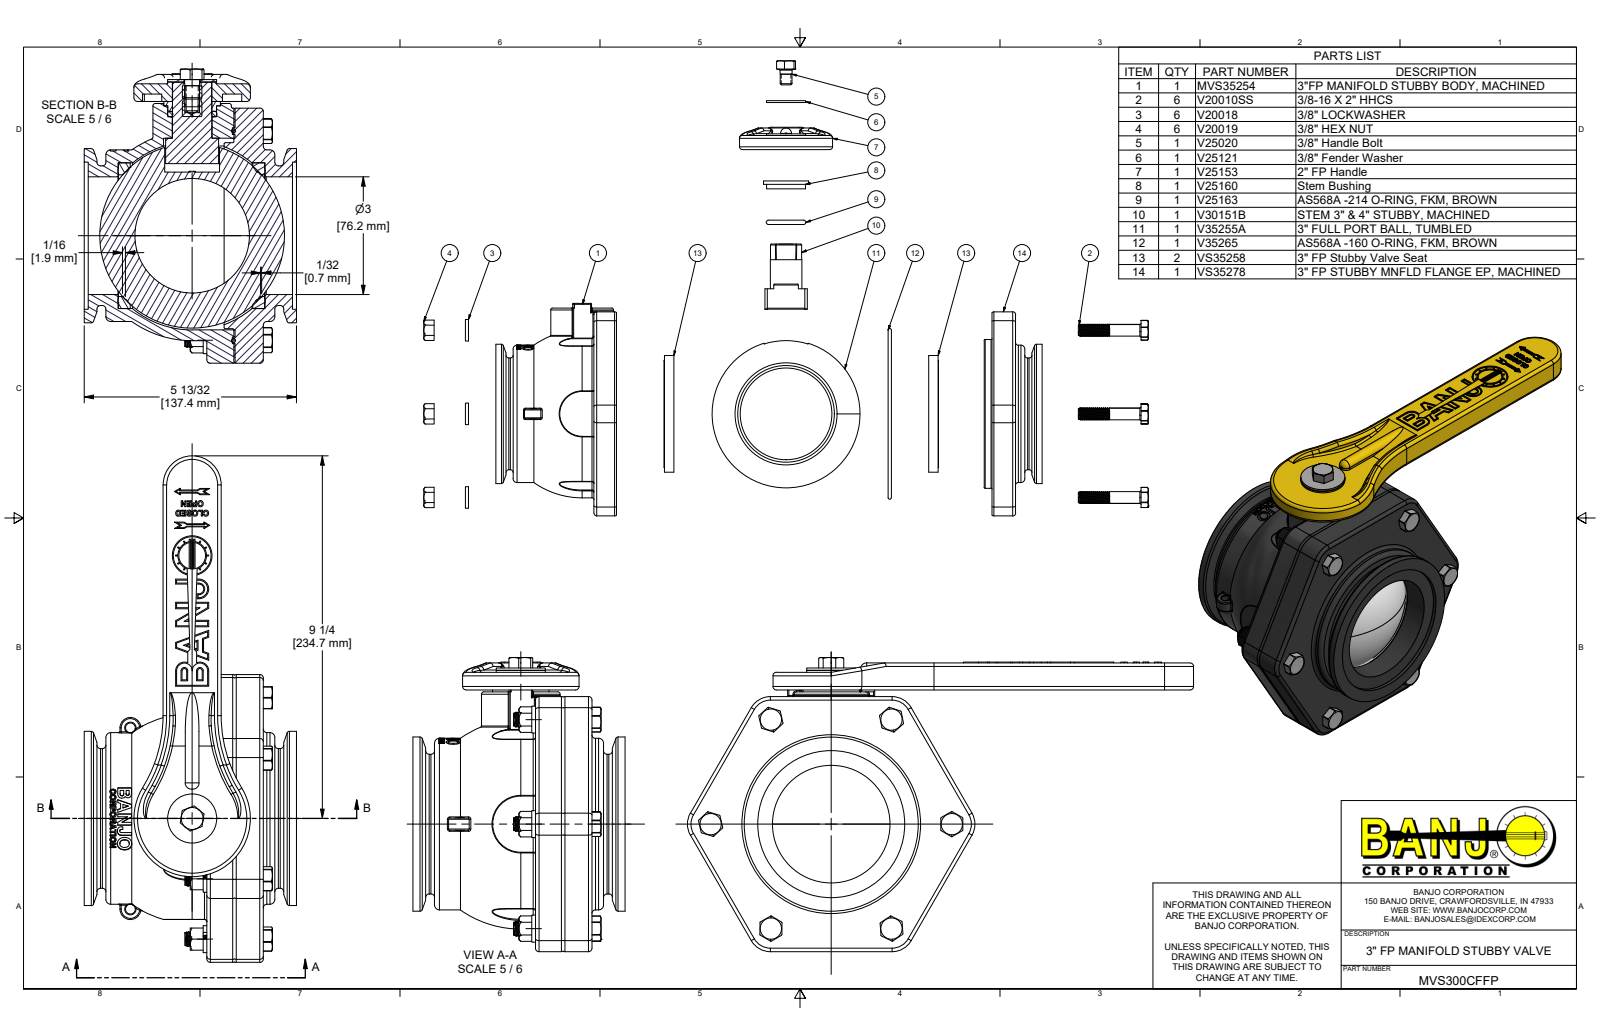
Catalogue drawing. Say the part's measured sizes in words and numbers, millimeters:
The part is named "MVS300CFFP; MVS35254; MVS35254X; VS35278 (+8 more)". Its 3-D file was written by "Autodesk Inventor 2019 (AUTOMOTIVE_DESIGN)". It is 32 solids with 2567 faces: 715 planar, 829 cylindrical and 1023 other. Overall it measures 327.8 by 190.4 by 137.4 millimeters. Its volume is 1 482 000 cubic millimeters and its surface area 345 500 square millimeters. Round holes: 6 of diameter 7.8, 6 of diameter 9.8, 6 of diameter 11.2, 3 of diameter 9.5, 2 of diameter 6.4, 1 of diameter 7.8, 1 of diameter 10.3, 1 of diameter 17.3, 1 of diameter 24.4, 1 of diameter 25.4, 1 of diameter 25.8, 1 of diameter 31.6. Round bosses or shafts: 90 of diameter 8.2, 7 of diameter 9.5, 6 of diameter 17.4, 1 of diameter 131.1, 1 of diameter 120.4, 1 of diameter 112.8, 1 of diameter 111.1, 1 of diameter 94.4. Partial cylindrical surfaces (rounded edges, fillets, slot ends): 32 of radius 2.3, 31 of radius 0.8, 12 of radius 4.1, 10 of radius 1.5, 6 of radius 0.8, 6 of radius 8.1, 6 of radius 14.3, 4 of radius 12.7. The main face-to-face distances are 18.3, 19.1, 17.5, 0.8, 36.6, 165.1, 11.4, 2.5, 134.9, 6.6. The hole center spacings are 78.1, 78.1, 135.3, 71, 156.2, 135.3, 170.2, 117.3.
